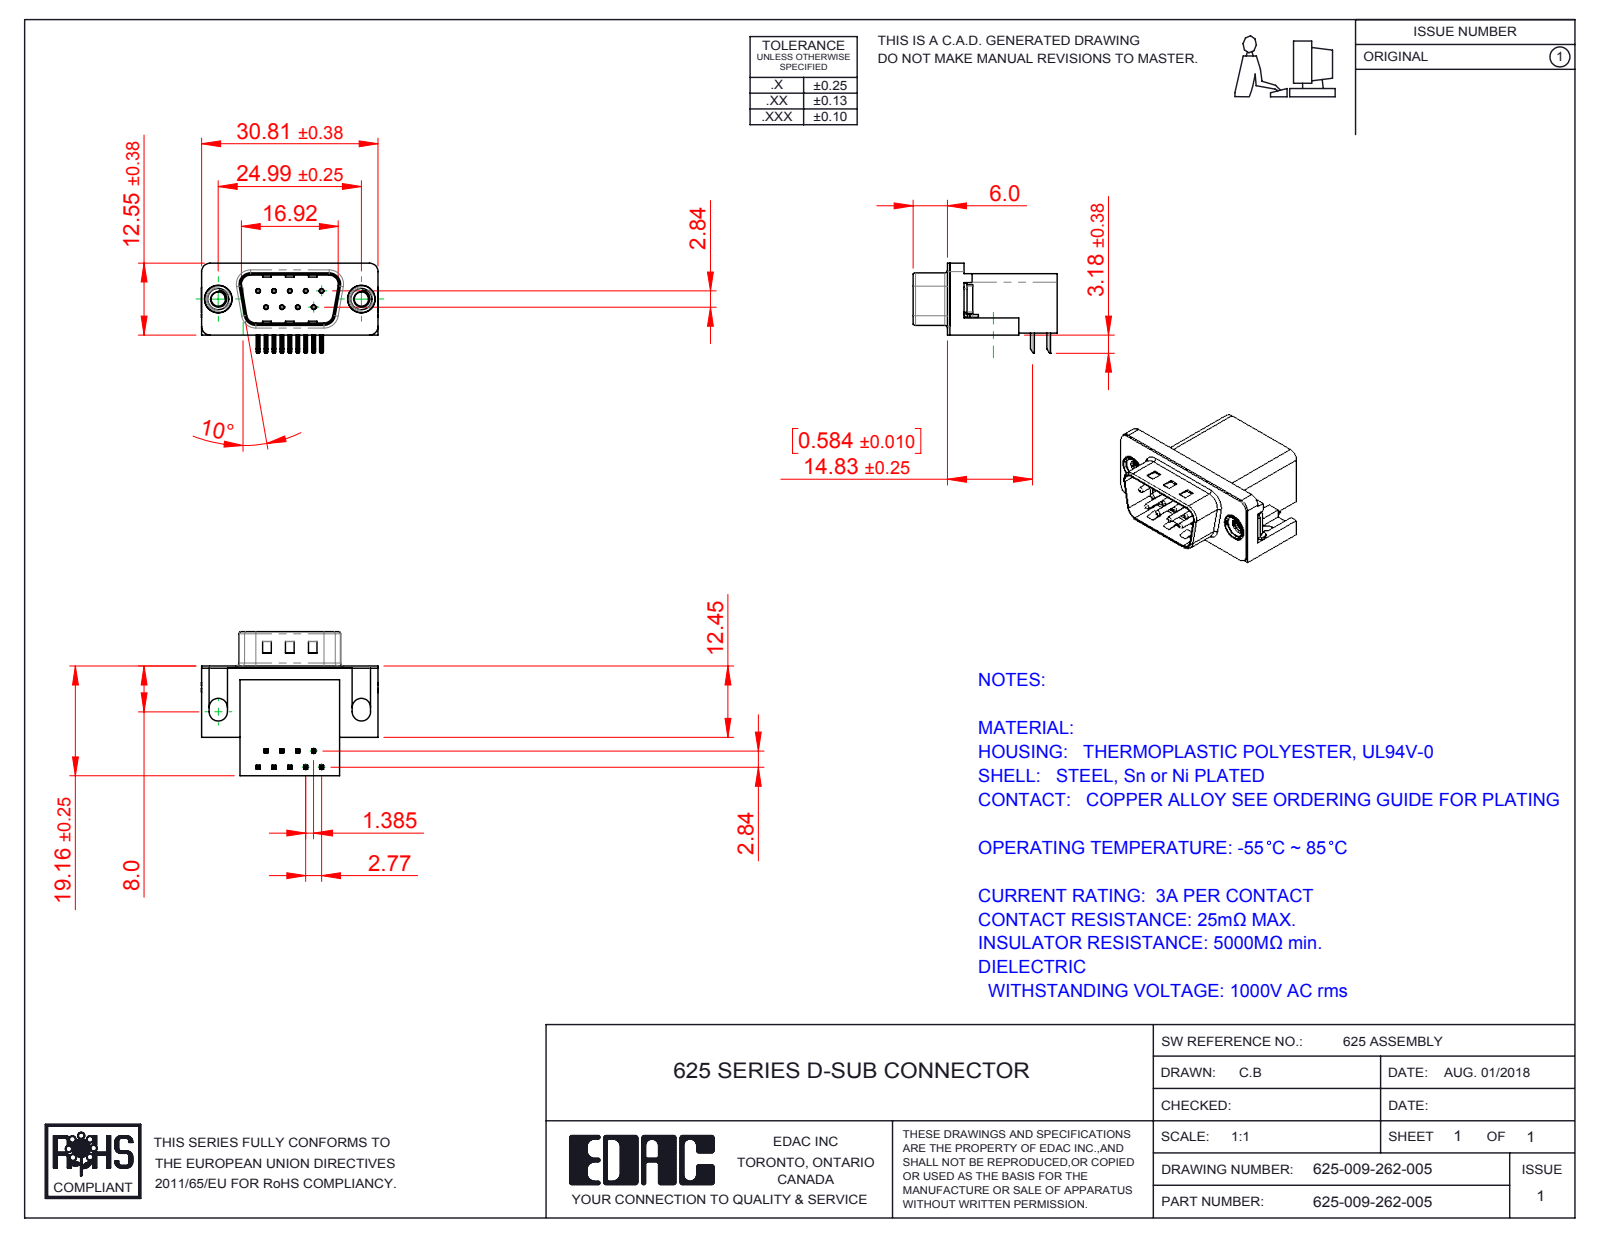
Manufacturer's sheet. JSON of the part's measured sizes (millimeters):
{"part_name": "625 M3 Threaded Rivet; 625 Non Board Mount; 625-009-262-005; 625 Housing_9 Socket (+3 more)", "step_written_by": "SolidWorks 2016 (CONFIG_CONTROL_DESIGN)", "units": "millimeters", "bodies": {"solids": 15, "faces": 991, "planar": 575, "cylindrical": 317, "other": 99}, "overall_size": [30.89, 25.16, 15.73], "volume_mm3": 4442, "surface_area_mm2": 4821, "round_holes": [[0.35, 9], [0.8, 9], [2.5, 2], [4, 2], [4.8, 2], [5, 2]], "round_bosses_or_shafts": [[0.75, 9], [4.9, 2], [4.75, 2], [3.9, 2]], "partial_cylinders_radius": [[0.25, 44], [0.12, 18], [1, 16], [0.5, 9], [1.5, 8], [1.6, 8], [0.9, 4], [2, 4]], "face_to_face_distances": [0.4, 10.34, 18.76, 19.16, 2.9, 16.26, 2.5, 0.35, 10.69, 6.7], "hole_center_spacings": [3.16, 2.77, 5.54, 5.03, 5.04, 8.31, 7.48, 7.49]}
